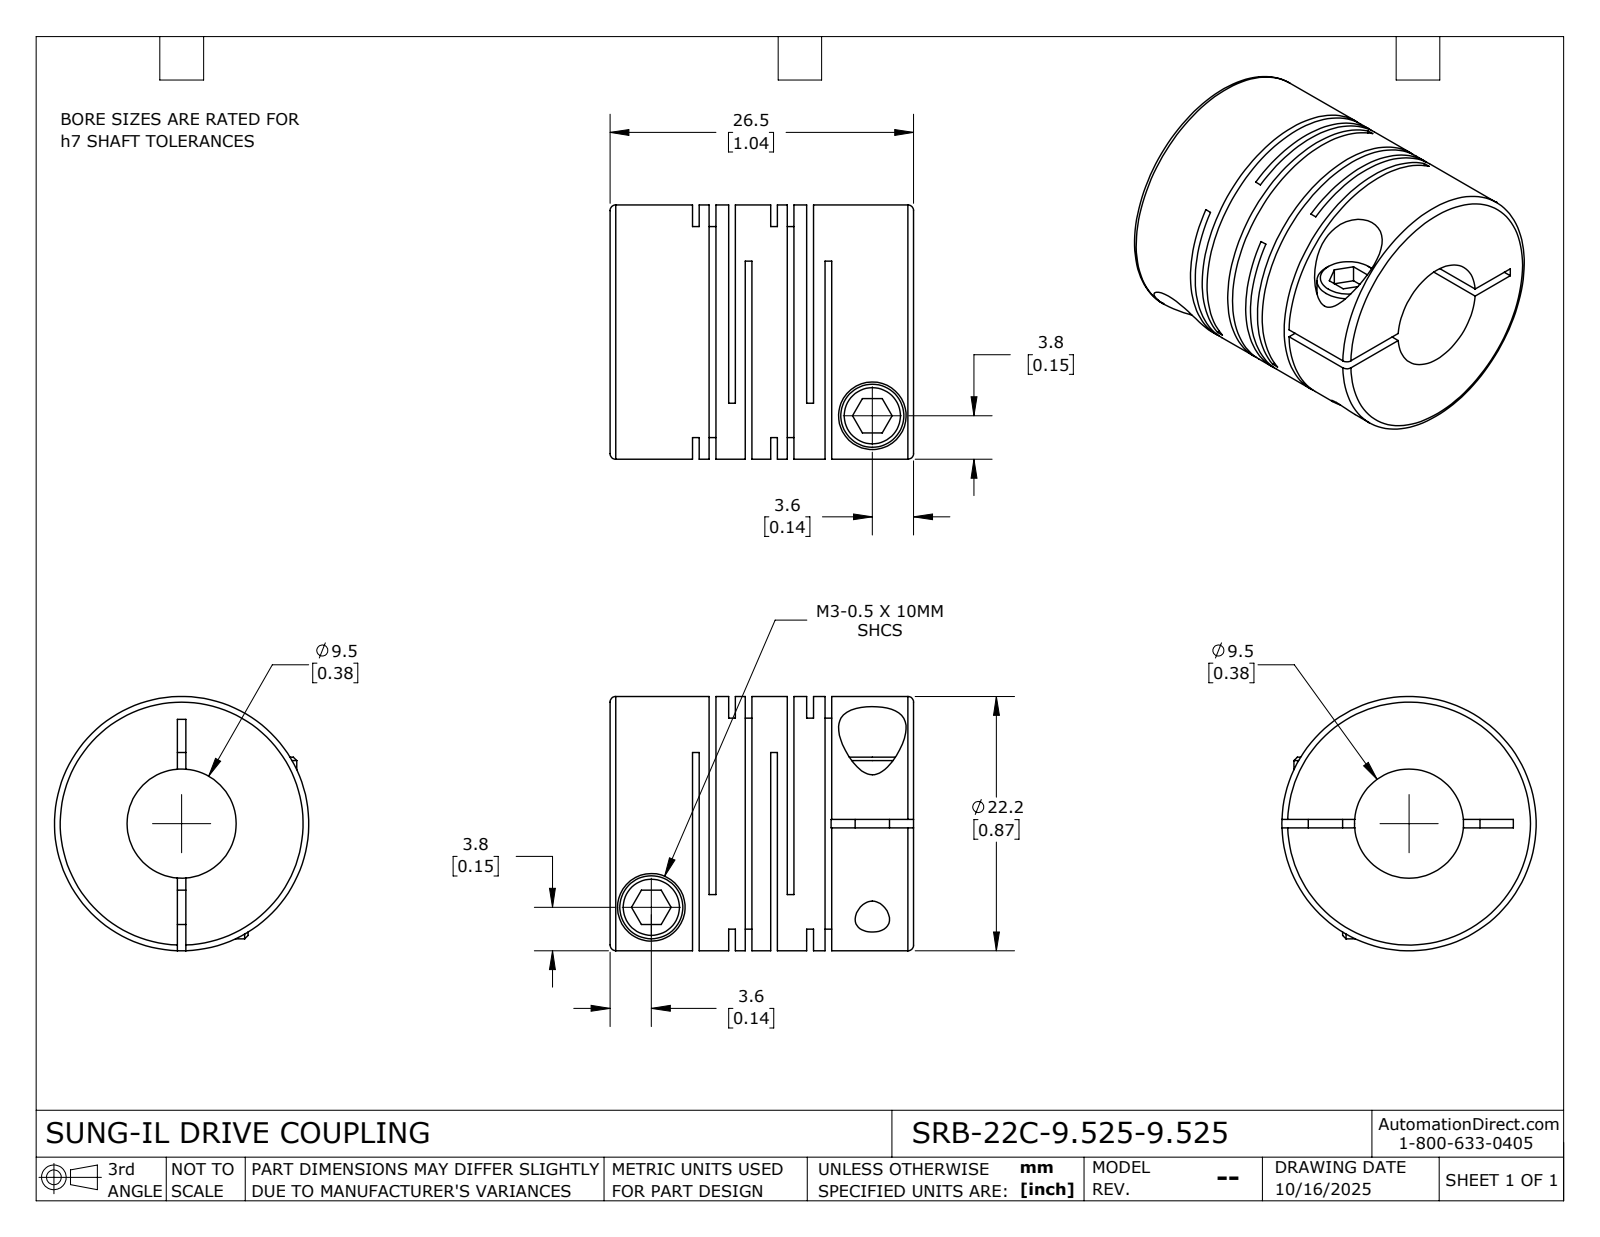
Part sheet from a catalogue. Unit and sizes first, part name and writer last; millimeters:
Units: millimetres
Overall size (bounding box): 26.5 × 22.2 × 22.2
Round holes (diameter × count): ⌀3 ×2, ⌀5.9 ×2, ⌀9.53 ×1
Round bosses / shafts (diameter × count): ⌀5.5 ×2, ⌀22.2 ×1
Main face-to-face distances: 0.59, 6.82, 1.45, 3.15, 5.37, 3.67, 1.7, 6.23, 2.56, 0.86
Volume: 6 875 mm³ · Surface area: 7 528 mm²
Bodies: 1 solid, 115 faces (60 planar, 42 cylindrical, 13 other)
Part name (STEP PRODUCT): SRB-22C-9.525-9.525
STEP written by: SolidWorks 2024 (CONFIG_CONTROL_DESIGN)
